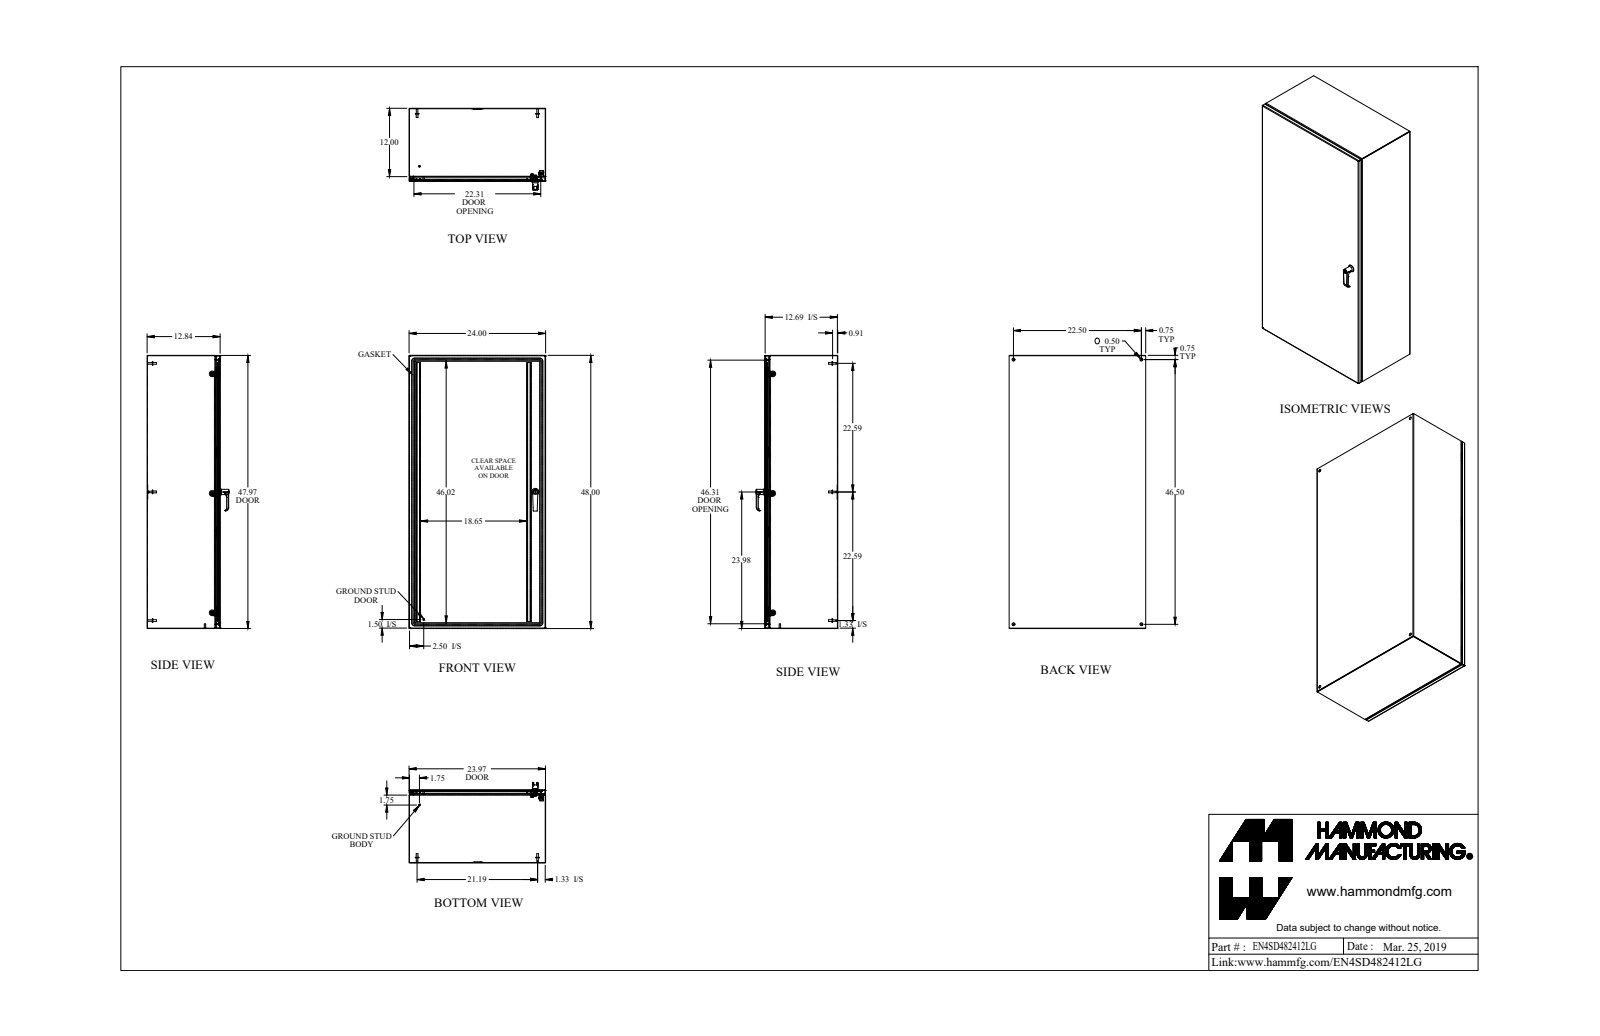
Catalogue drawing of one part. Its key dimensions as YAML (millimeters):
part_name: "EN4SD482412LG"
step_written_by: "SolidWorks 2018 (AUTOMOTIVE_DESIGN)"
units: millimeters
bodies: {solids: 55, faces: 1443, planar: 632, cylindrical: 532, other: 279}
overall_size: [1219.2, 609.6, 364.9]
volume: 5572000
surface_area: 6095000
round_holes:
  - {diameter: 4.5, count: 6}
  - {diameter: 12.7, count: 4}
  - {diameter: 5, count: 3}
  - {diameter: 6.4, count: 3}
  - {diameter: 6.7, count: 3}
  - {diameter: 10.5, count: 3}
  - {diameter: 6.5, count: 2}
  - {diameter: 8, count: 2}
  - {diameter: 10, count: 2}
  - {diameter: 4.4, count: 1}
  - {diameter: 6.1, count: 1}
  - {diameter: 6.1, count: 1}
round_bosses_or_shafts:
  - {diameter: 6.4, count: 7}
  - {diameter: 15.9, count: 6}
  - {diameter: 9.5, count: 6}
  - {diameter: 8, count: 6}
  - {diameter: 6.9, count: 6}
  - {diameter: 4, count: 6}
  - {diameter: 25.4, count: 3}
  - {diameter: 16, count: 2}
partial_cylinders:
  - {radius: 0.9, count: 18}
  - {radius: 2.7, count: 18}
  - {radius: 0.8, count: 15}
  - {radius: 1.1, count: 12}
  - {radius: 2.1, count: 12}
  - {radius: 0.2, count: 8}
  - {radius: 1.2, count: 8}
  - {radius: 1.6, count: 8}
face_to_face_distances: [1.8, 324.2, 322.4, 326.1, 607.8, 605.9, 609.6, 1.8, 1215.5, 1217.4]
hole_center_spacings: [20, 532.9, 533.1, 533.4, 547.3, 571.5, 1066, 1066]
